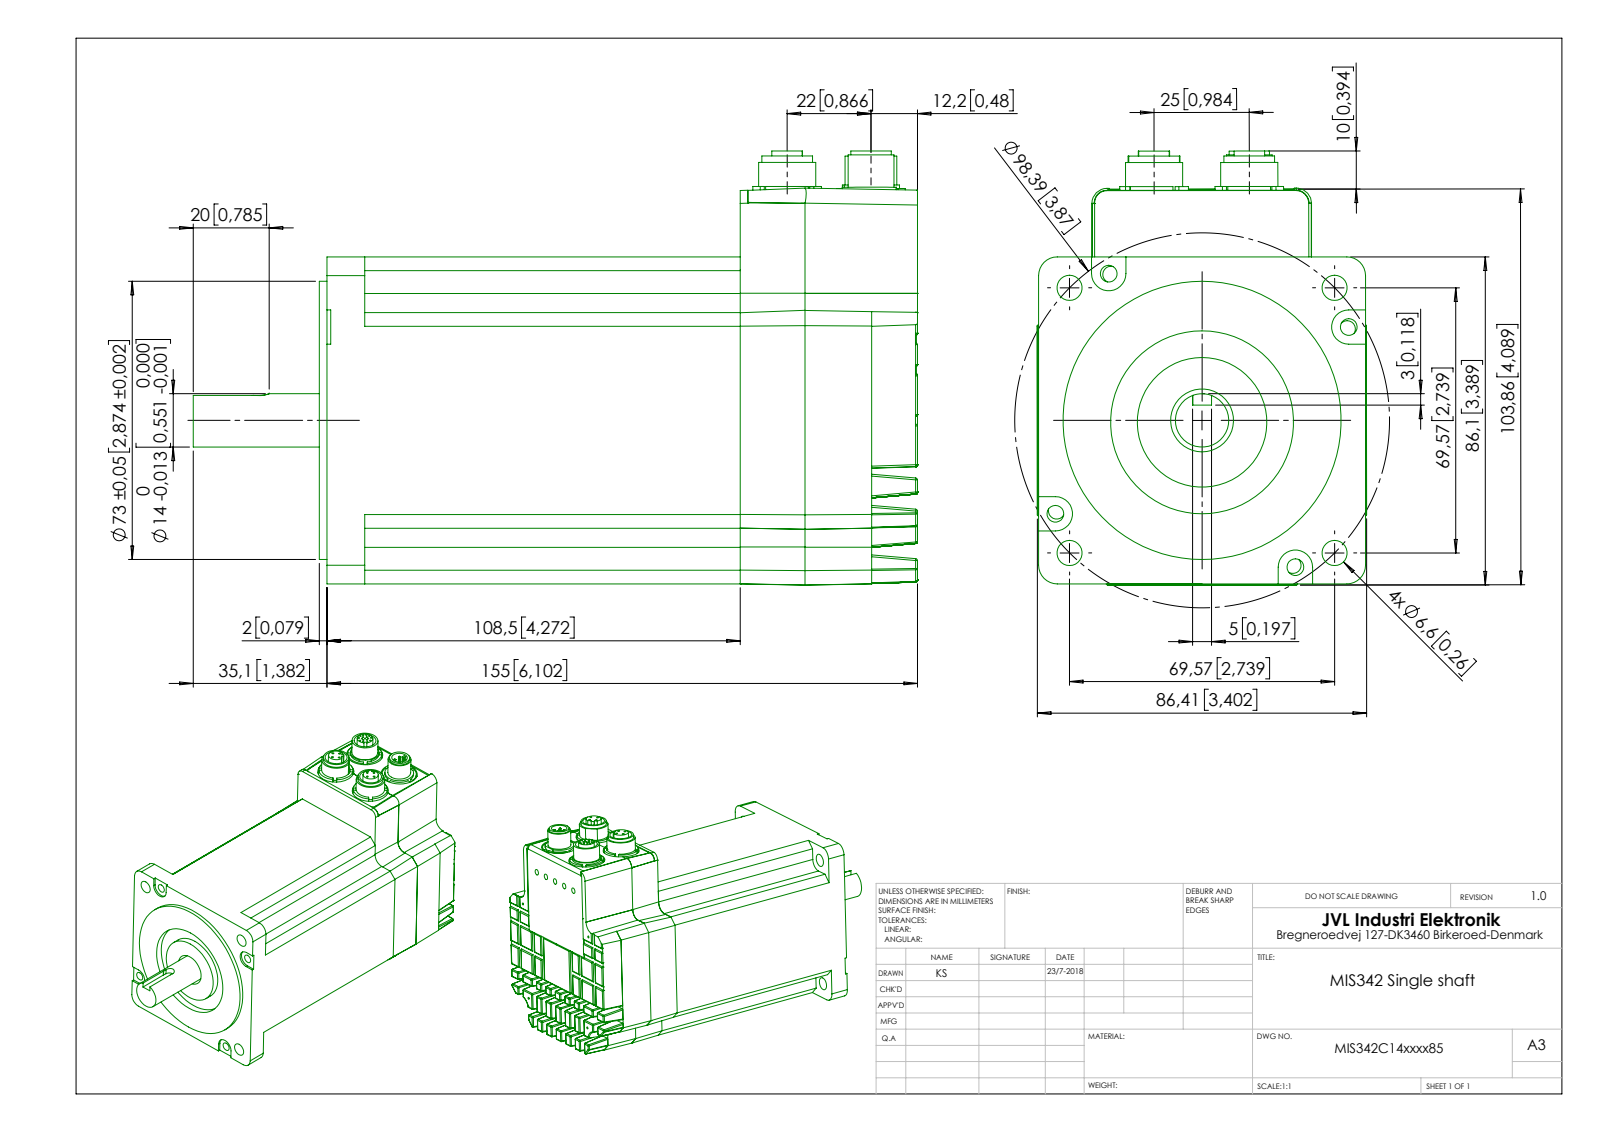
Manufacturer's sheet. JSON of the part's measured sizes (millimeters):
{"part_name": "MIS342C14xxxx85; MIS342 motor single shaft; MIS34 house; MM3831 (+4 more)", "step_written_by": "Solid Edge (AP242_MANAGED_MODEL_BASED_3D_ENGINEERING_MIM_LF)", "units": "millimeters", "bodies": {"solids": 7, "faces": 1070, "planar": 484, "cylindrical": 418, "other": 168}, "overall_size": [190.1, 114.53, 86.41], "volume_mm3": 1046000, "surface_area_mm2": 130875, "round_holes": [[0.7, 17], [1, 12], [3, 5], [4.3, 4], [4.4, 4], [6.6, 4], [19, 4], [11.5, 3], [8.2, 1], [16, 1], [16.5, 1], [48, 1]], "round_bosses_or_shafts": [[1, 5], [18, 4], [15, 3], [8.2, 3], [13.3, 2], [8, 2], [73, 1], [34, 1]], "partial_cylinders_radius": [[0.5, 164], [4.5, 4], [4.9, 4], [5, 4], [0.48, 3], [2, 3], [7.5, 3], [0.2, 2]], "face_to_face_distances": [85.8, 17, 1, 18, 14.6, 17.4, 0.6, 16.4, 71.2, 110.5], "hole_center_spacings": [3.25, 3.54, 1.63, 1.65, 3.24, 1.44, 2.48, 2.52]}
